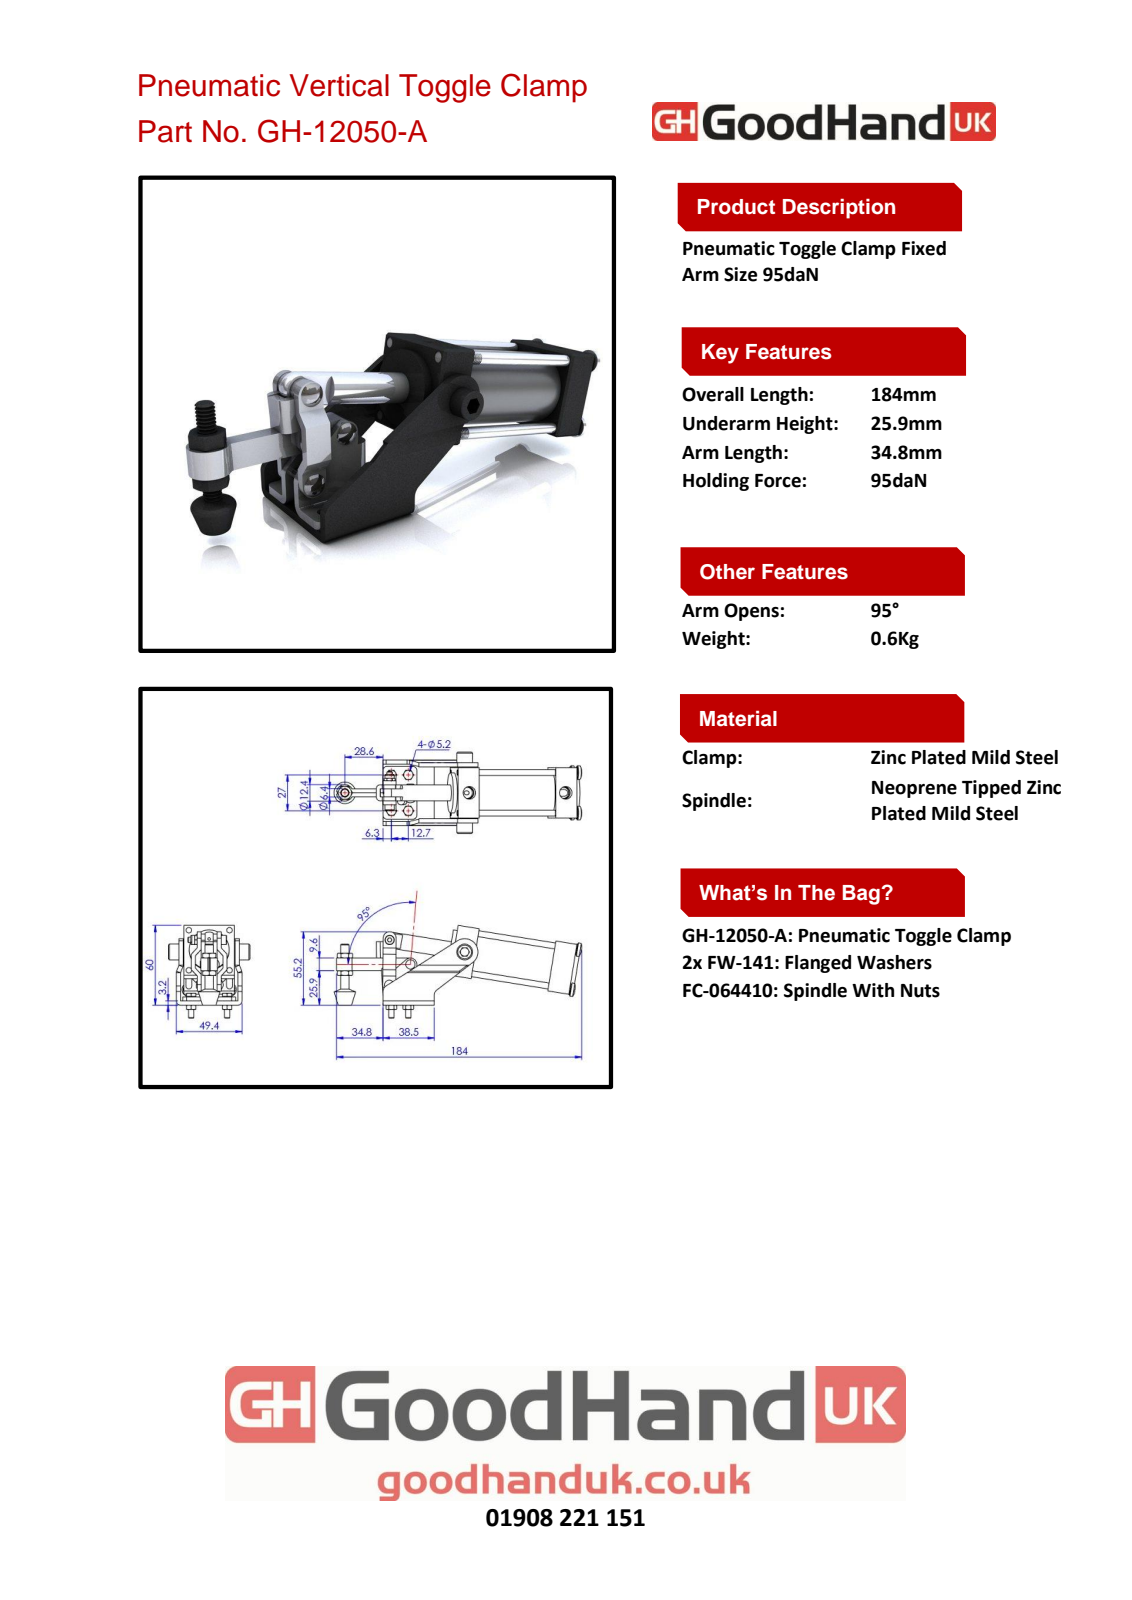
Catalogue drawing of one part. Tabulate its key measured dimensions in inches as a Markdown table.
| quantity | value |
| --- | --- |
| part name | Group4^GH-12050-A(簡化); 11205008-1^GH-12050-A(簡化); GH-12050-A(簡化); Group2^GH-12050-A(簡化) (+4 more) |
| STEP written by | SolidWorks 2016 (AUTOMOTIVE_DESIGN) |
| units | inches |
| bodies | 9 solids, 799 faces (366 planar, 205 cylindrical, 228 other) |
| overall size | 7.32 × 2.749 × 2.412 |
| volume | 7.853 in³ |
| surface area | 95.07 in² |
| round holes (diameter × count) | 0.118 × 4, 0.236 × 2, 0.311 × 2, 0.472 × 2, 0.197 × 1, 0.252 × 1, 1.181 × 1 |
| round bosses / shafts (diameter × count) | 0.276 × 5, 0.157 × 5, 0.406 × 4, 0.177 × 4, 1.181 × 3, 1.378 × 1, 0.472 × 1, 0.469 × 1 |
| partial cylindrical surfaces (radius × count) | 0.118 × 10, 0.126 × 6, 0.079 × 4, 0.197 × 3, 0.039 × 2, 0.177 × 2, 0.193 × 2, 0.059 × 1 |
| main face-to-face distances | 0.118, 0.126, 0.236, 0.354, 0.63, 0.866, 0.512, 0.984, 0.748, 0.079 |
| hole center spacings | 0.603, 0.606, 0.724, 0.869, 0.95, 1.327, 1.646, 2.24 |
